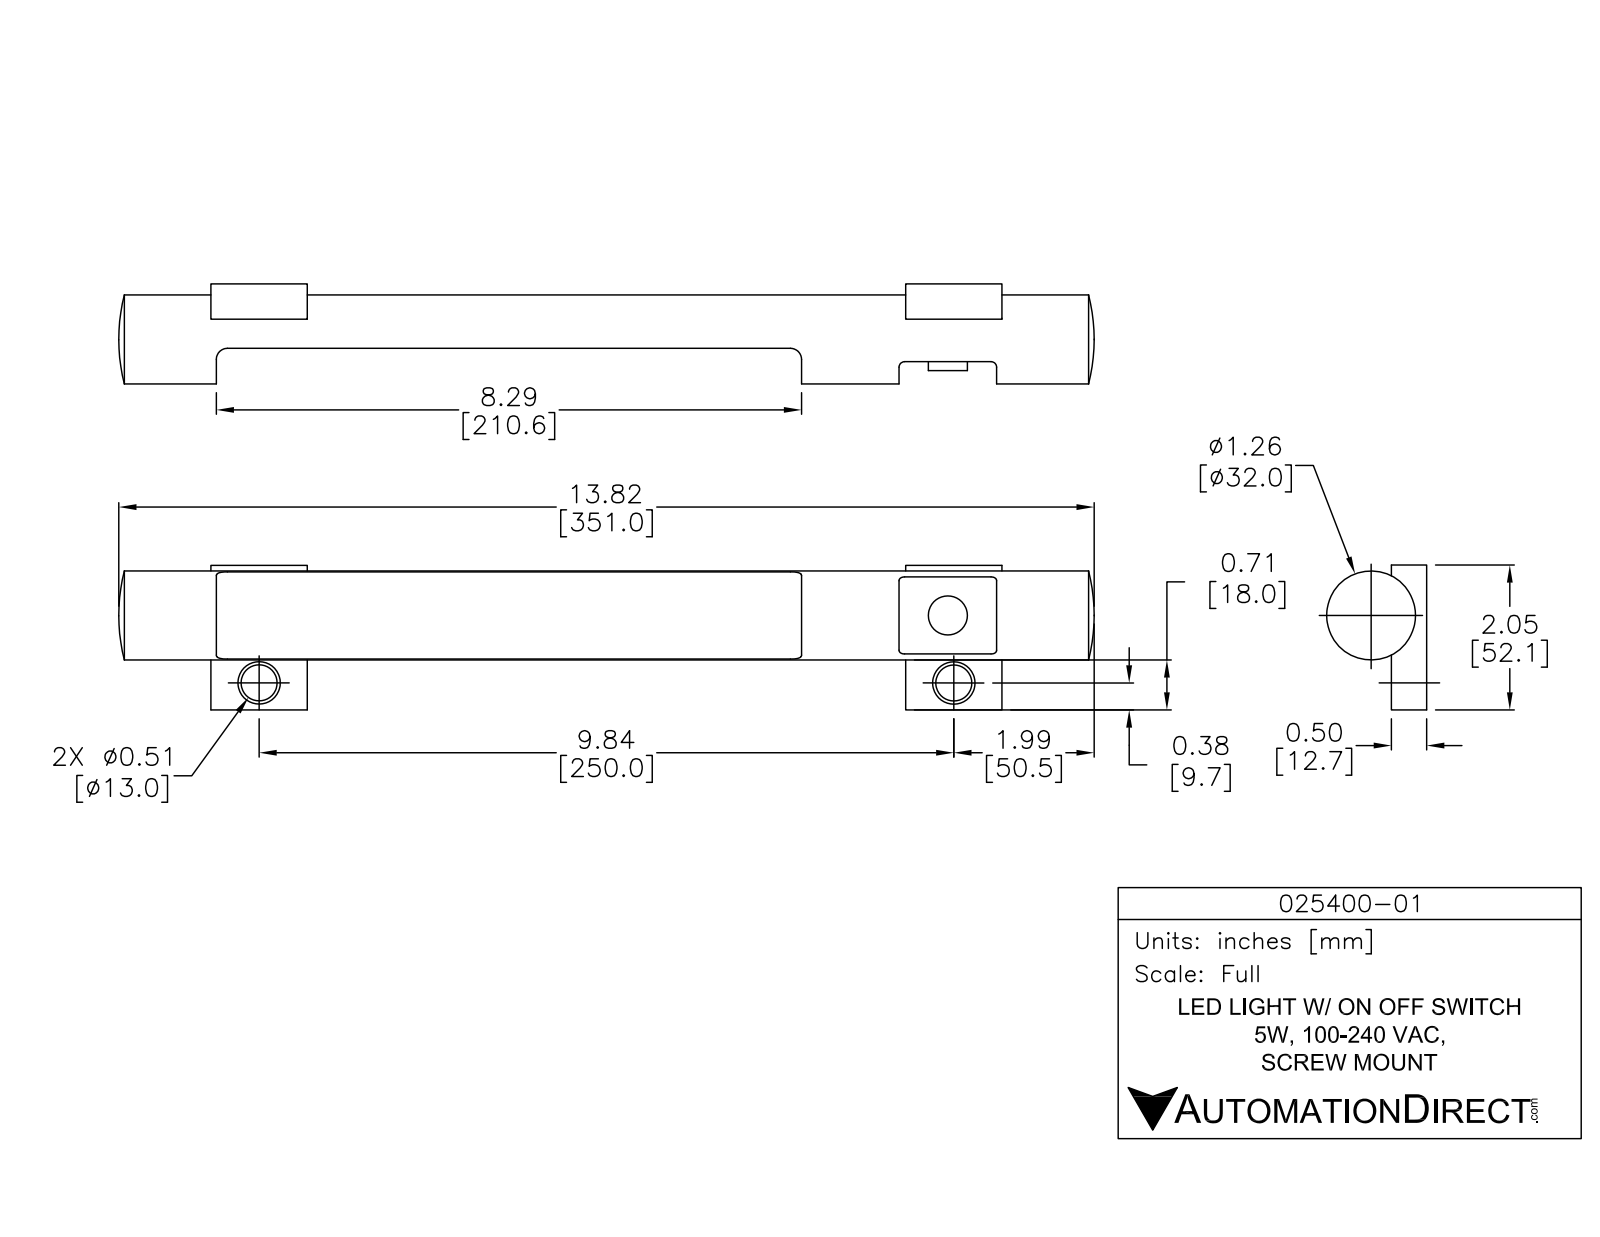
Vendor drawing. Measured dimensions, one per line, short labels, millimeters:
name: 025400-01
written by: SolidWorks 2013 (AUTOMOTIVE_DESIGN)
unit: mm
bodies: 1 solid, 176 faces (99 planar, 35 cylindrical, 42 other)
size: 349.5 × 51.1 × 34.8
volume: 239 400 mm³; area: 42 400 mm²
holes: 2× ⌀2, 2× ⌀5.8
bosses: 2× ⌀1.9, 1× ⌀32
rounds: 4× R1.5, 4× R2.6, 4× R5.1, 2× R3, 2× R16, 1× R0.8, 1× R30.7
face distances: 23, 51.1, 0.8, 13.8, 5.6, 8.3, 11.4, 2.5, 0.8, 14
hole spacings: 5.1, 248.9
